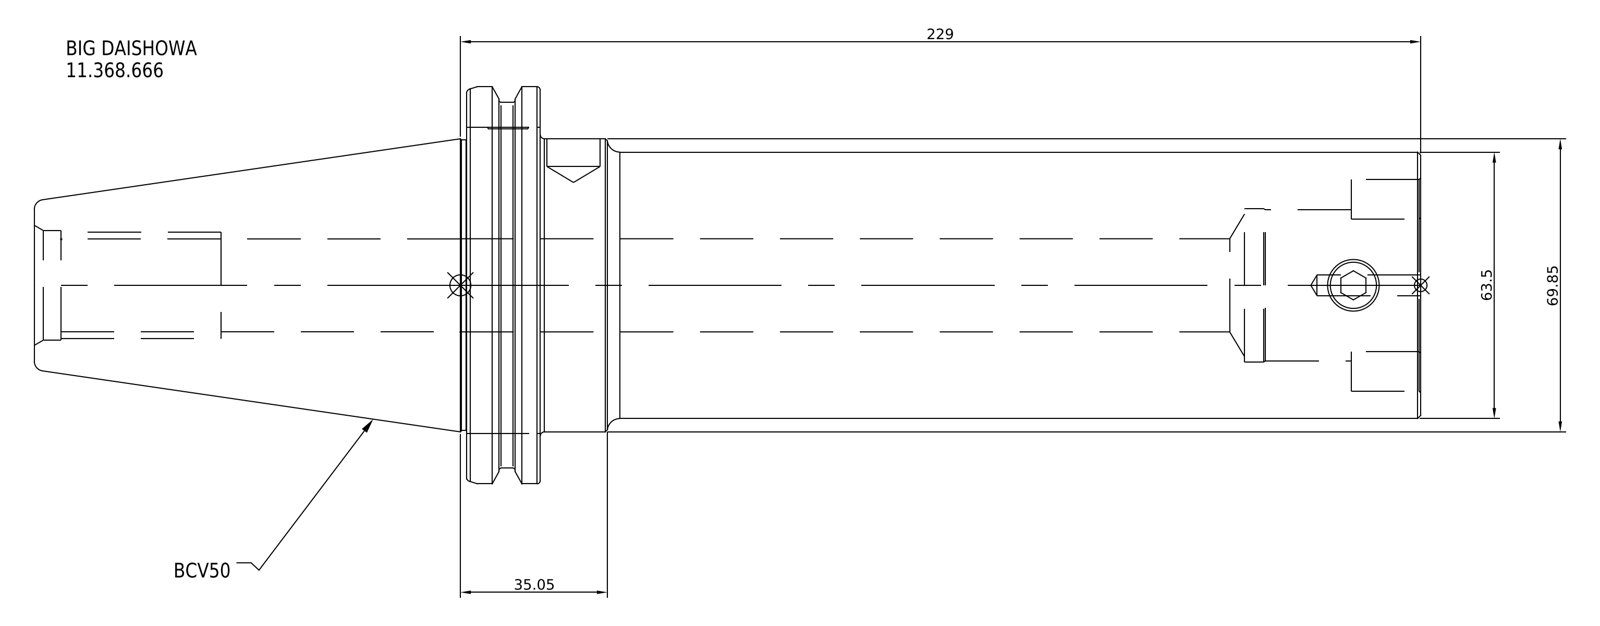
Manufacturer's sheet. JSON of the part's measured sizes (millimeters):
{"part_name": "11.368.666", "step_written_by": "SolidWorks 2021 (CONFIG_CONTROL_DESIGN)", "units": "millimeters", "bodies": {"solids": 1, "faces": 16, "planar": 7, "cylindrical": 6, "other": 3}, "overall_size": [330.6, 98.43, 98.43], "volume_mm3": 1057000, "surface_area_mm2": 79674, "round_bosses_or_shafts": [[98.43, 1], [91.29, 1], [69.85, 1], [63.5, 1]], "face_to_face_distances": [17.55, 209.95, 227.5, 330.6, 120.65, 103.1, 194, 15.95, 33.5, 136.6]}
